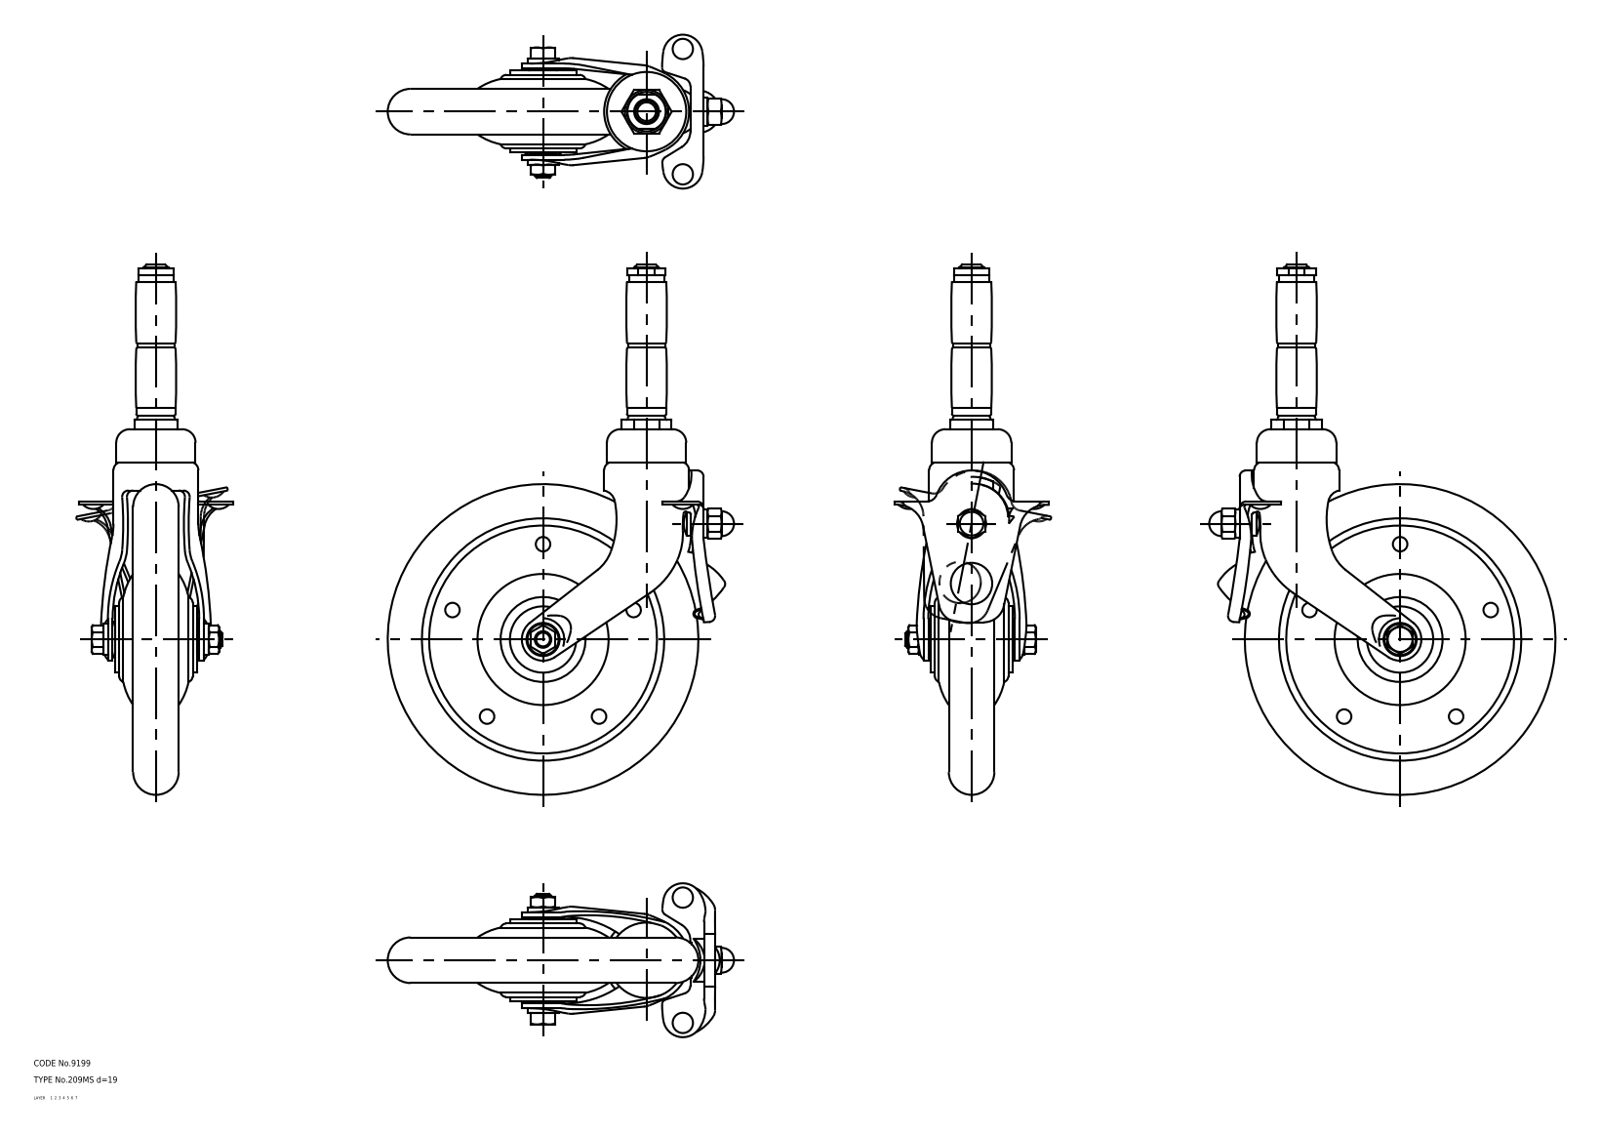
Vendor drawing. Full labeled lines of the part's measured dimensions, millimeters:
Part name (STEP PRODUCT): lever; wheel; main shaft; axle (+1 more)
STEP written by: CADfix (AUTOMOTIVE_DESIGN)
Units: millimetres
Bodies: 5 solids, 497 faces (0 planar, 0 cylindrical, 497 other)
Overall size (bounding box): 256 × 167.2 × 74.3
Volume: 375 950 mm³ · Surface area: 94 498 mm²
